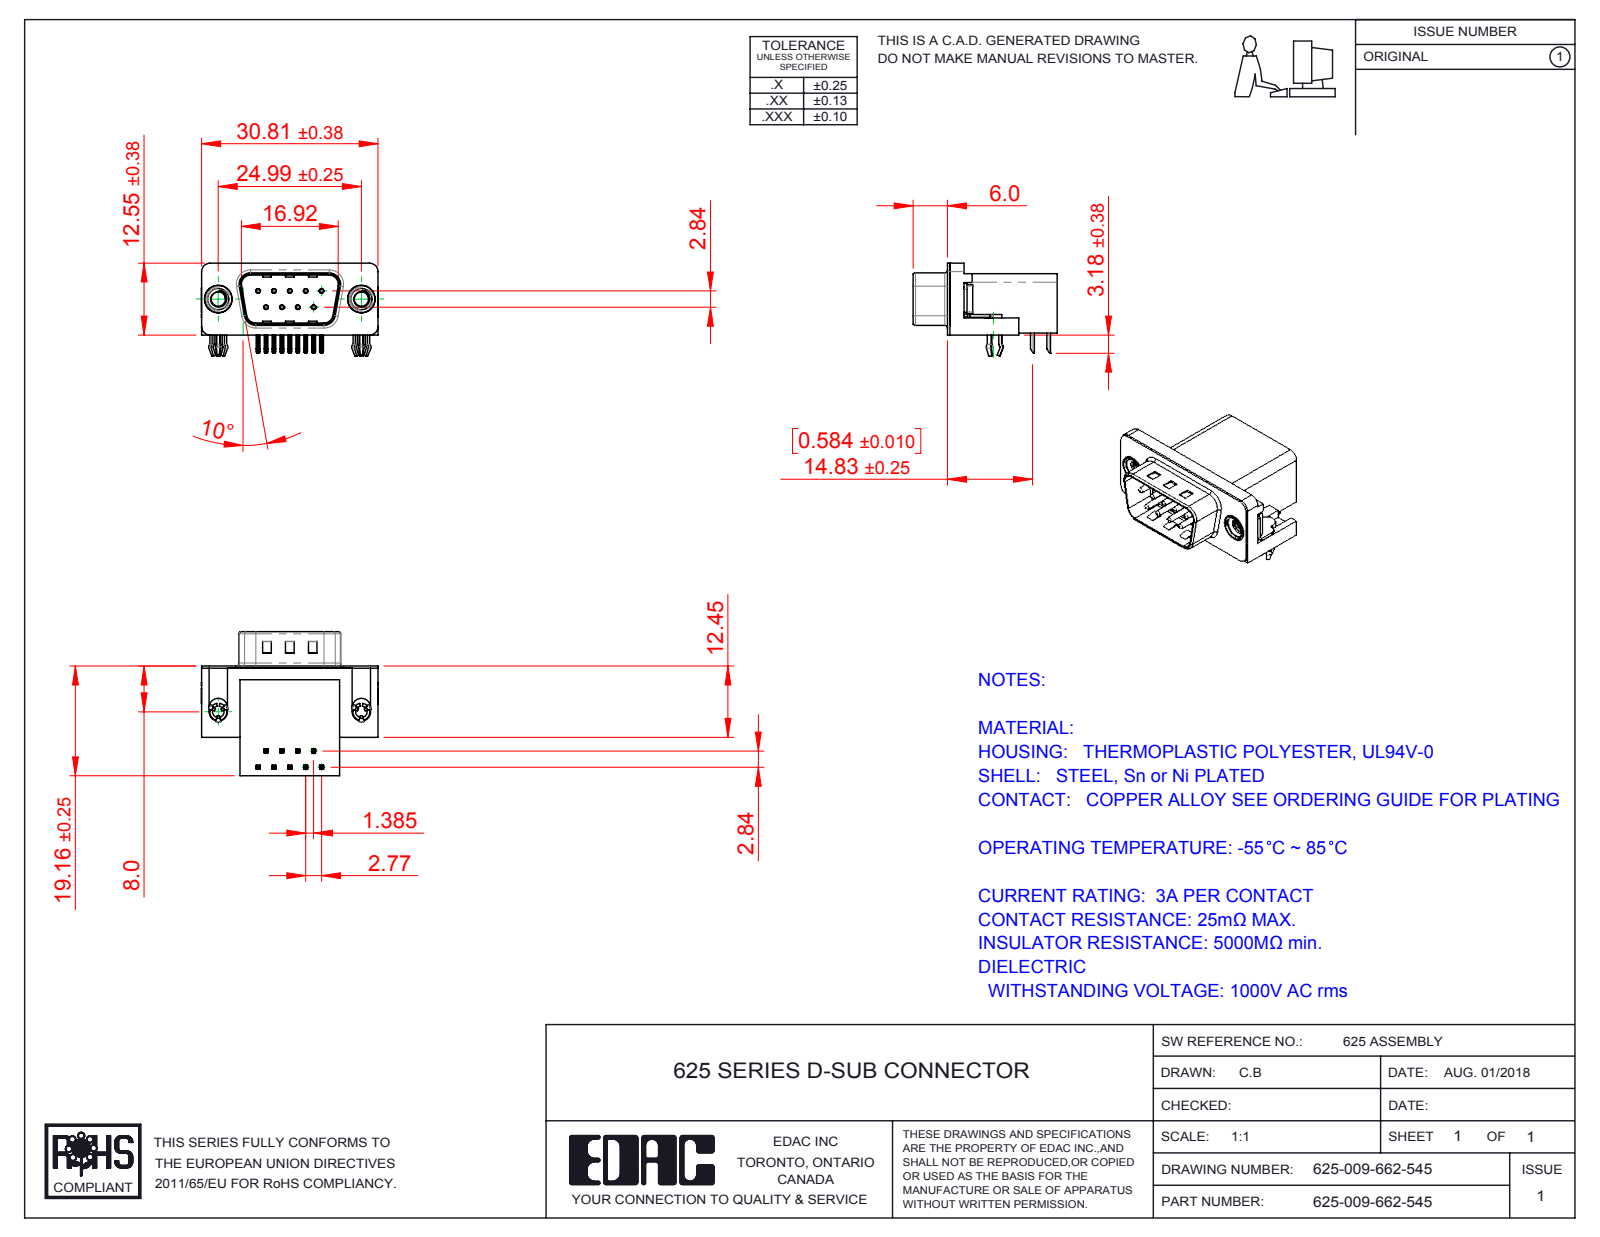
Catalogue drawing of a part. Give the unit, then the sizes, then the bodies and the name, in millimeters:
Units: millimetres
Overall size (bounding box): 30.89 × 25.16 × 16.25
Round holes (diameter × count): ⌀0.35 ×9, ⌀0.8 ×9, ⌀2 ×2, ⌀2.5 ×2, ⌀4 ×2, ⌀4.8 ×2, ⌀5 ×2
Round bosses / shafts (diameter × count): ⌀0.75 ×9, ⌀4.9 ×2, ⌀4.75 ×2, ⌀3.9 ×2, ⌀3 ×2
Partial cylindrical surfaces — rounded edges, fillets, slot ends (radius × count): R0.25 ×48, R0.12 ×18, R1 ×16, R0.5 ×9, R1.5 ×8, R1.6 ×8, R0.9 ×4, R2 ×4
Main face-to-face distances: 0.4, 10.34, 18.76, 19.16, 2.9, 16.26, 2.5, 0.35, 10.69, 6.7
Hole centre spacings: 3.16, 2.77, 5.54, 5.03, 5.04, 8.31, 7.48, 7.49
Volume: 4 479 mm³ · Surface area: 5 016 mm²
Bodies: 15 solids, 1097 faces (611 planar, 327 cylindrical, 159 other)
Part name (STEP PRODUCT): 625 3 Prong Board Lock; 625 Shell_9 Socket; 625 Contact Top; 625-009-662-545 (+3 more)
STEP written by: SolidWorks 2016 (CONFIG_CONTROL_DESIGN)
